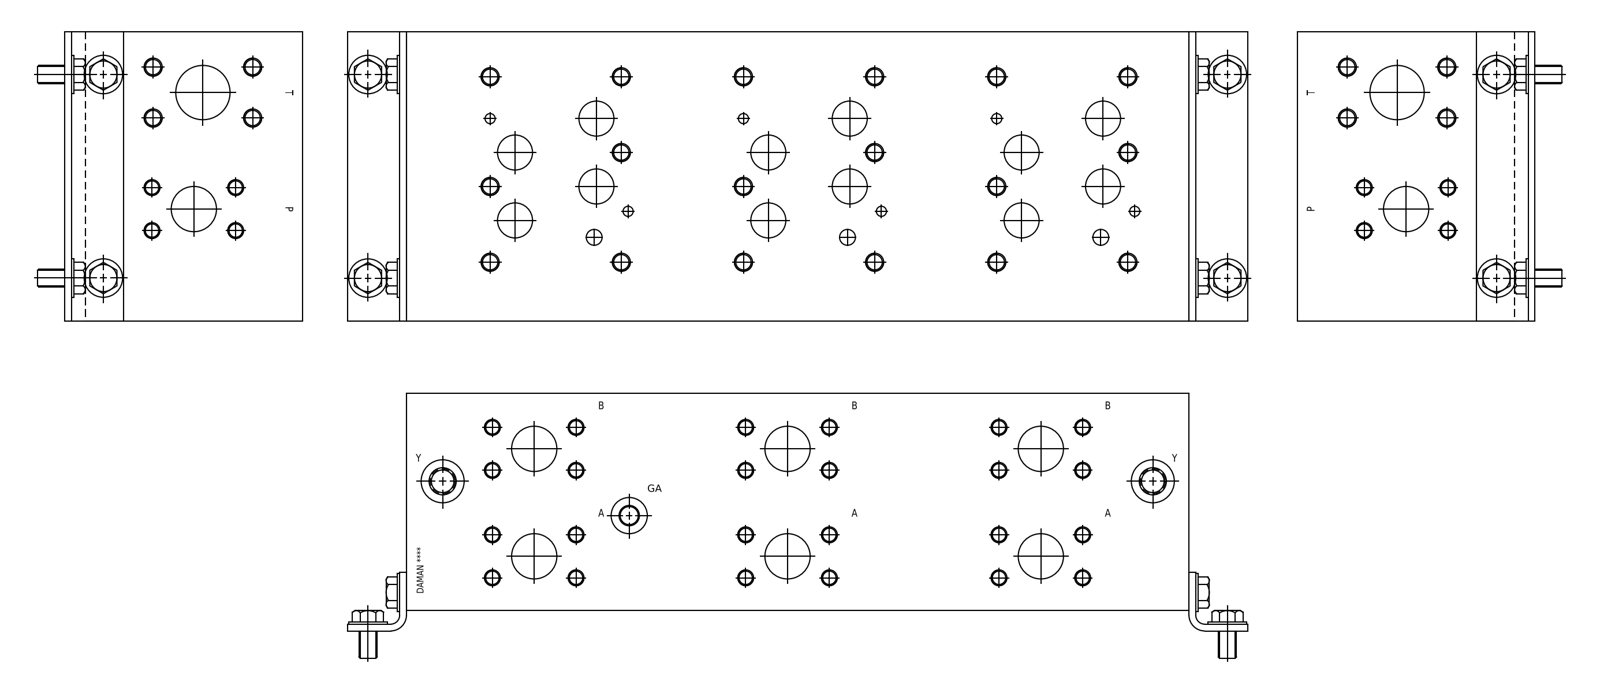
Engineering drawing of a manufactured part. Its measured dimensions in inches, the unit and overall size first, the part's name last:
Units: inches
Overall size (bounding box): 21.625 × 8 × 6
Round holes (diameter × count): ⌀0.438 ×34, ⌀0.368 ×31, ⌀0.5 ×26, ⌀0.422 ×24, ⌀0.906 ×12, ⌀1.25 ×7, ⌀0.281 ×6, ⌀0.689 ×2, ⌀0.75 ×2, ⌀0.758 ×2, ⌀1.206 ×2, ⌀0.484 ×1
Main face-to-face distances: 6, 8, 21.625, 0.031, 7.969, 1.11, 1.079, 6.89, 4.81, 1.19
Hole centre spacings: 7, 1.3, 14, 1.188, 2.969, 3.746, 7.604, 2.312
Volume: 1 014 in³ · Surface area: 853 in²
Bodies: 1 solid, 888 faces (455 planar, 170 cylindrical, 263 other)
Part name (STEP PRODUCT): Part_AD08HP037F_3D
STEP written by: Autodesk Inventor 2021 (AUTOMOTIVE_DESIGN)
